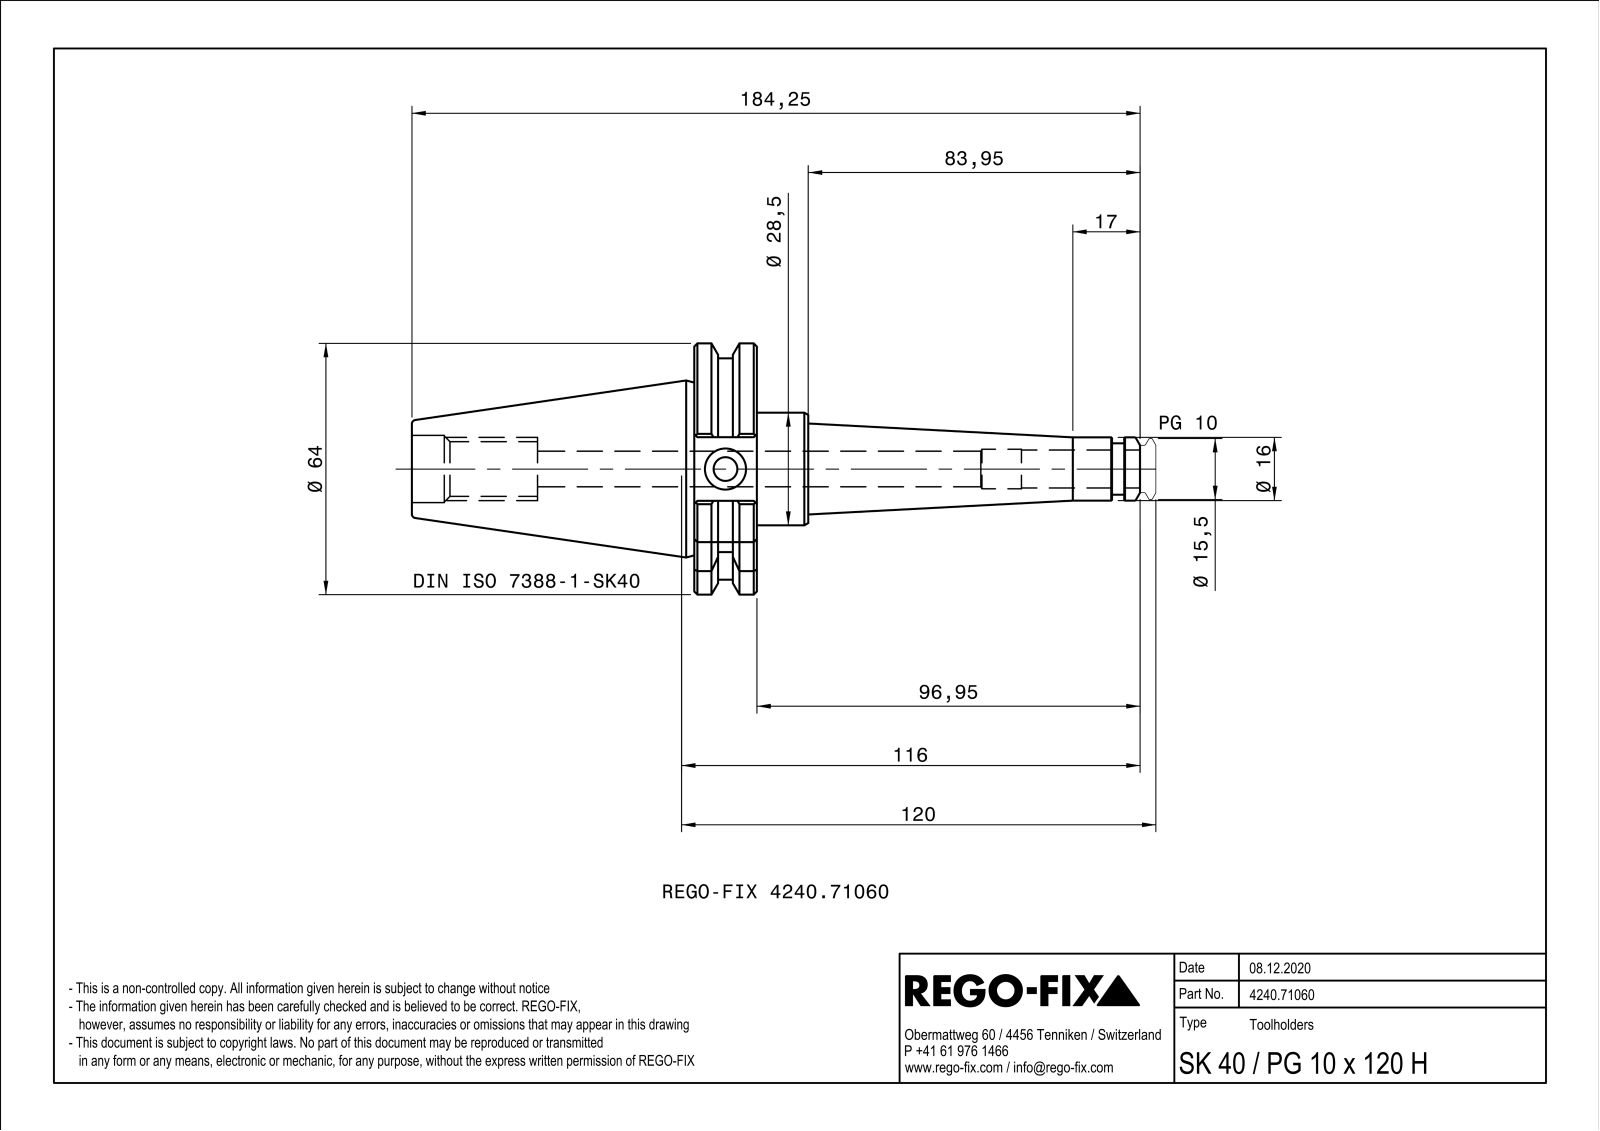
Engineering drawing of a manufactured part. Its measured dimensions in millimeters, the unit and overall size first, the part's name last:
Units: millimetres
Overall size (bounding box): 184.25 × 63.55 × 61.01
Round holes (diameter × count): ⌀3.5 ×5, ⌀10 ×2, ⌀6 ×1, ⌀9 ×1, ⌀13.84 ×1, ⌀17 ×1
Round bosses / shafts (diameter × count): ⌀28.5 ×1, ⌀16 ×1, ⌀13 ×1
Partial cylindrical surfaces — rounded edges, fillets, slot ends (radius × count): R0.5 ×13, R28 ×1, R31.77 ×1
Main face-to-face distances: 15.85, 47.3, 16.1, 87.3, 71.45, 10.45, 26.55, 6.35, 40.95, 9.83
Volume: 120 825 mm³ · Surface area: 30 007 mm²
Bodies: 1 solid, 144 faces (44 planar, 45 cylindrical, 55 other)
Part name (STEP PRODUCT): NOCUT
STEP written by: SIEMENS PLM Software Solid Edge ST10 (AUTOMOTIVE_DESIGN)
